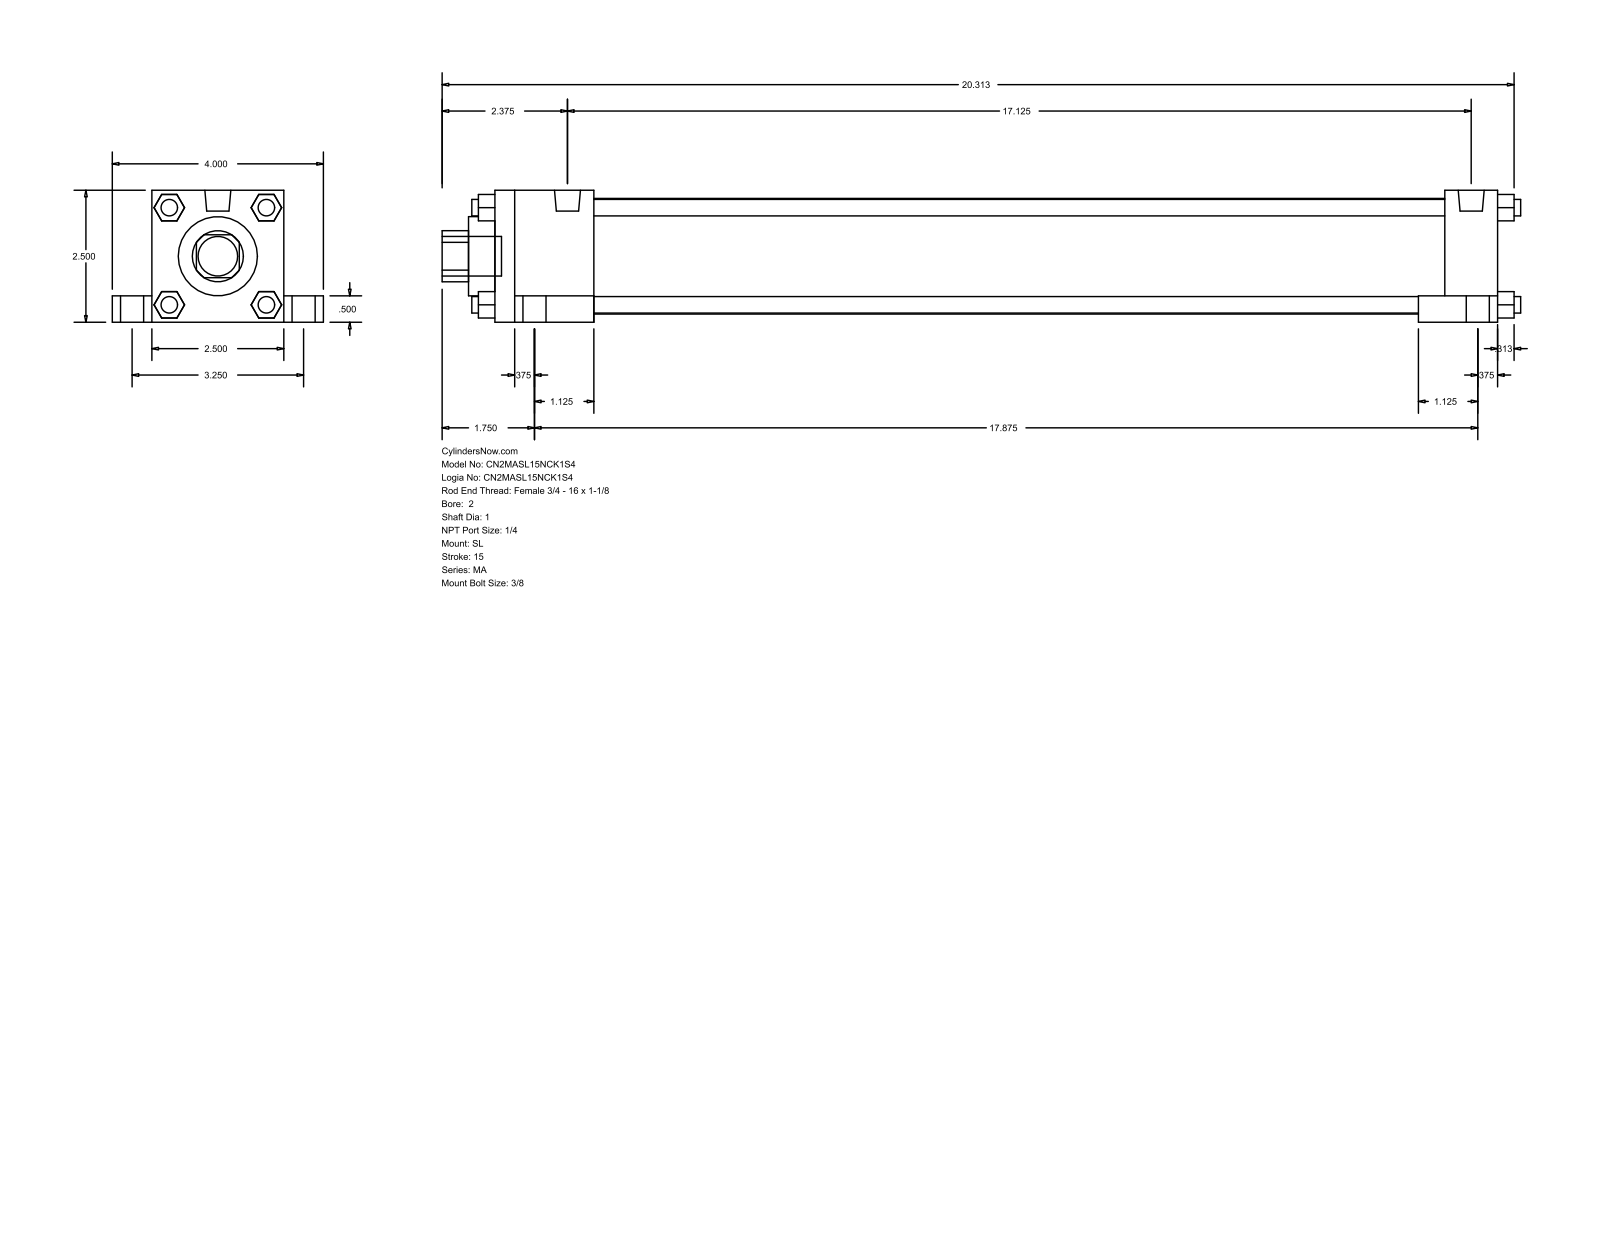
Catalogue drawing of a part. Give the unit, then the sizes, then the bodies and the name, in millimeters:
Units: millimetres
Overall size (bounding box): 519.11 × 101.6 × 63.5
Round holes (diameter × count): ⌀25.4 ×1, ⌀38.1 ×1, ⌀55.63 ×1
Round bosses / shafts (diameter × count): ⌀7.94 ×8, ⌀17.46 ×4, ⌀11.11 ×4, ⌀12.49 ×2, ⌀19.05 ×1
Partial cylindrical surfaces — rounded edges, fillets, slot ends (radius × count): R12.29 ×1
Main face-to-face distances: 63.5, 12.7, 482.6, 19.05, 82.55, 25.4, 50.8, 47.63, 434.97, 457.2
Bodies: 0 solids, 148 faces (112 planar, 36 cylindrical, 0 other)
Part name (STEP PRODUCT): MA_SL__0200_1
STEP written by: GSSL Pune (CONFIG_CONTROL_DESIGN)
